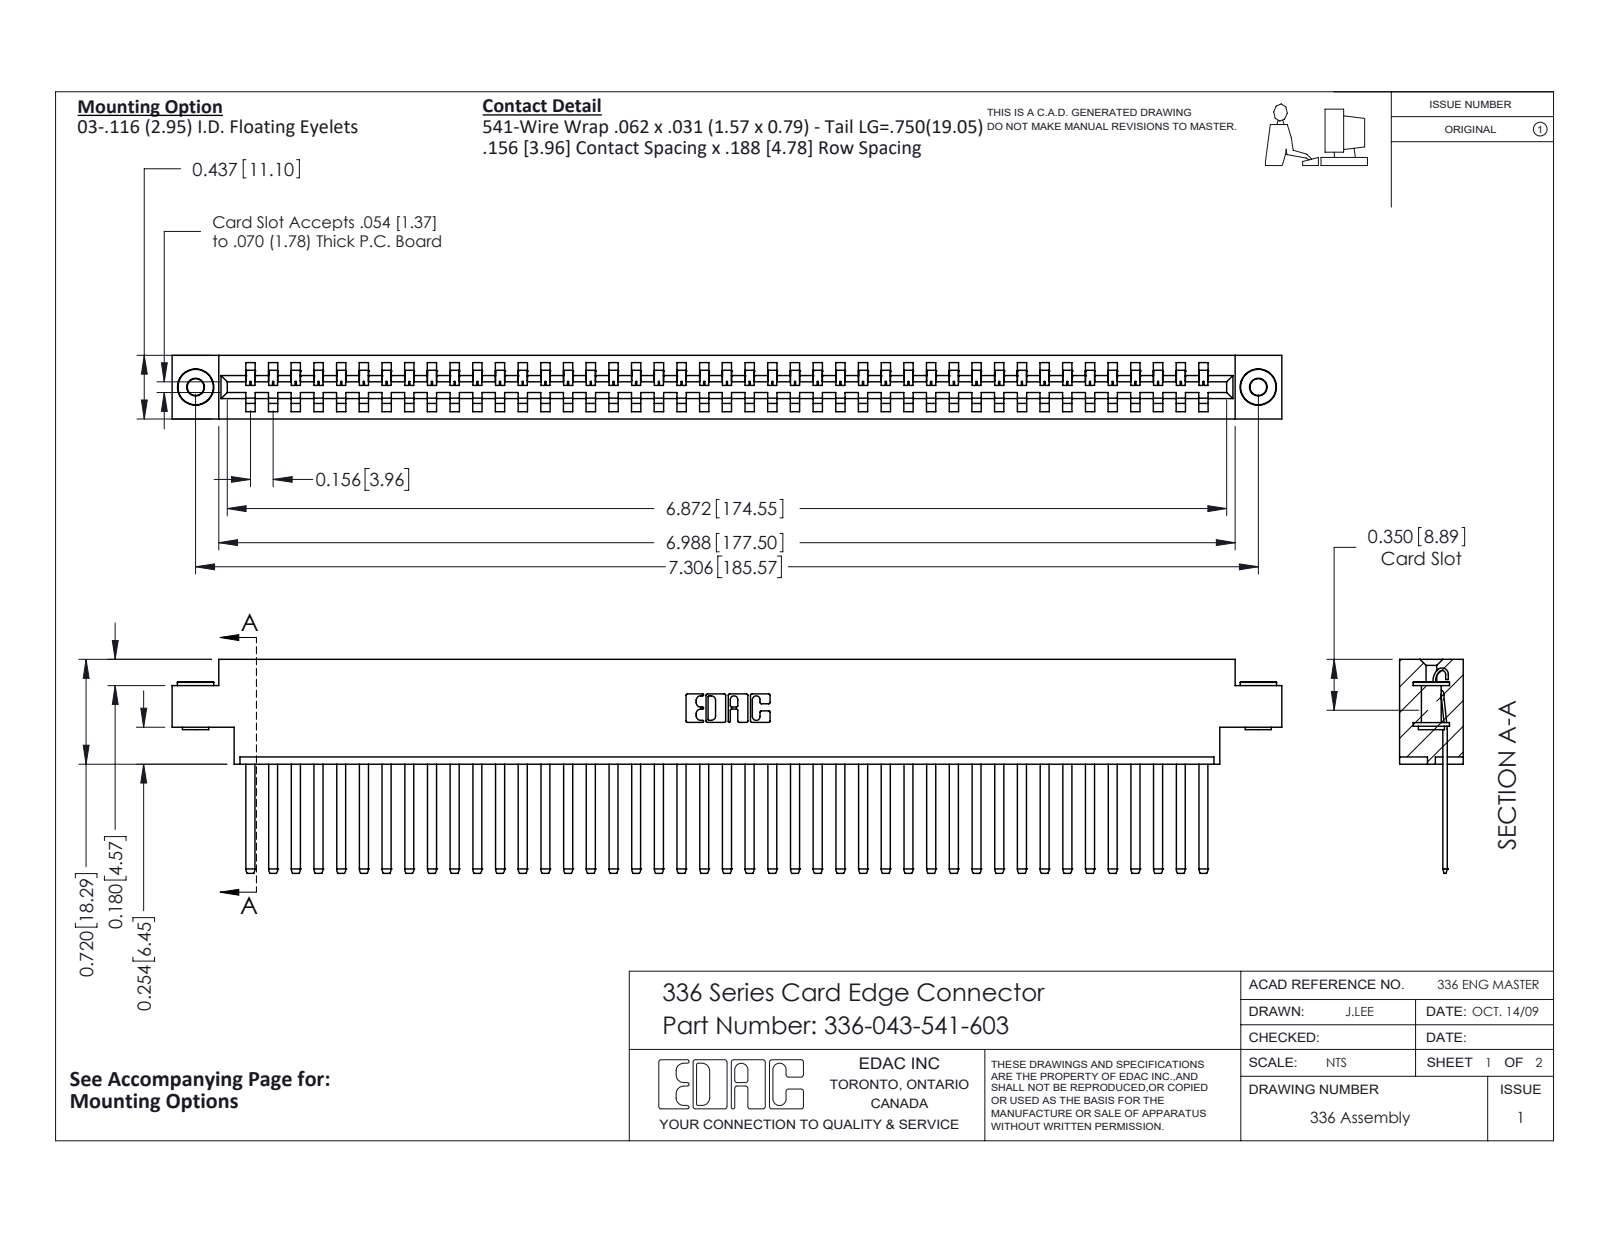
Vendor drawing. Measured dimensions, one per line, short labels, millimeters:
name: 336 Part_Offset - .156 Dia - TH; 336-290-001_336-290-541; 336-043-541-603; 345-250-002_345-250-002-102
written by: SolidWorks 2020 (CONFIG_CONTROL_DESIGN)
unit: mm
bodies: 46 solids, 2306 faces (1546 planar, 752 cylindrical, 8 other)
size: 193.8 × 37.3 × 11.1
volume: 28 280 mm³; area: 31 110 mm²
holes: 2× ⌀2.9, 2× ⌀4
bosses: 2× ⌀6.4, 2× ⌀4.6, 2× ⌀3.5
rounds: 86× R0.1, 86× R1.4, 22× R0.3, 6× R0.2, 6× R0.8, 3× R0.7, 2× R0.6, 2× R1
face distances: 11.1, 0.8, 4.6, 8.3, 3.6, 7.5, 2.8, 6.5, 1.3, 9.8
hole spacings: 185.6
